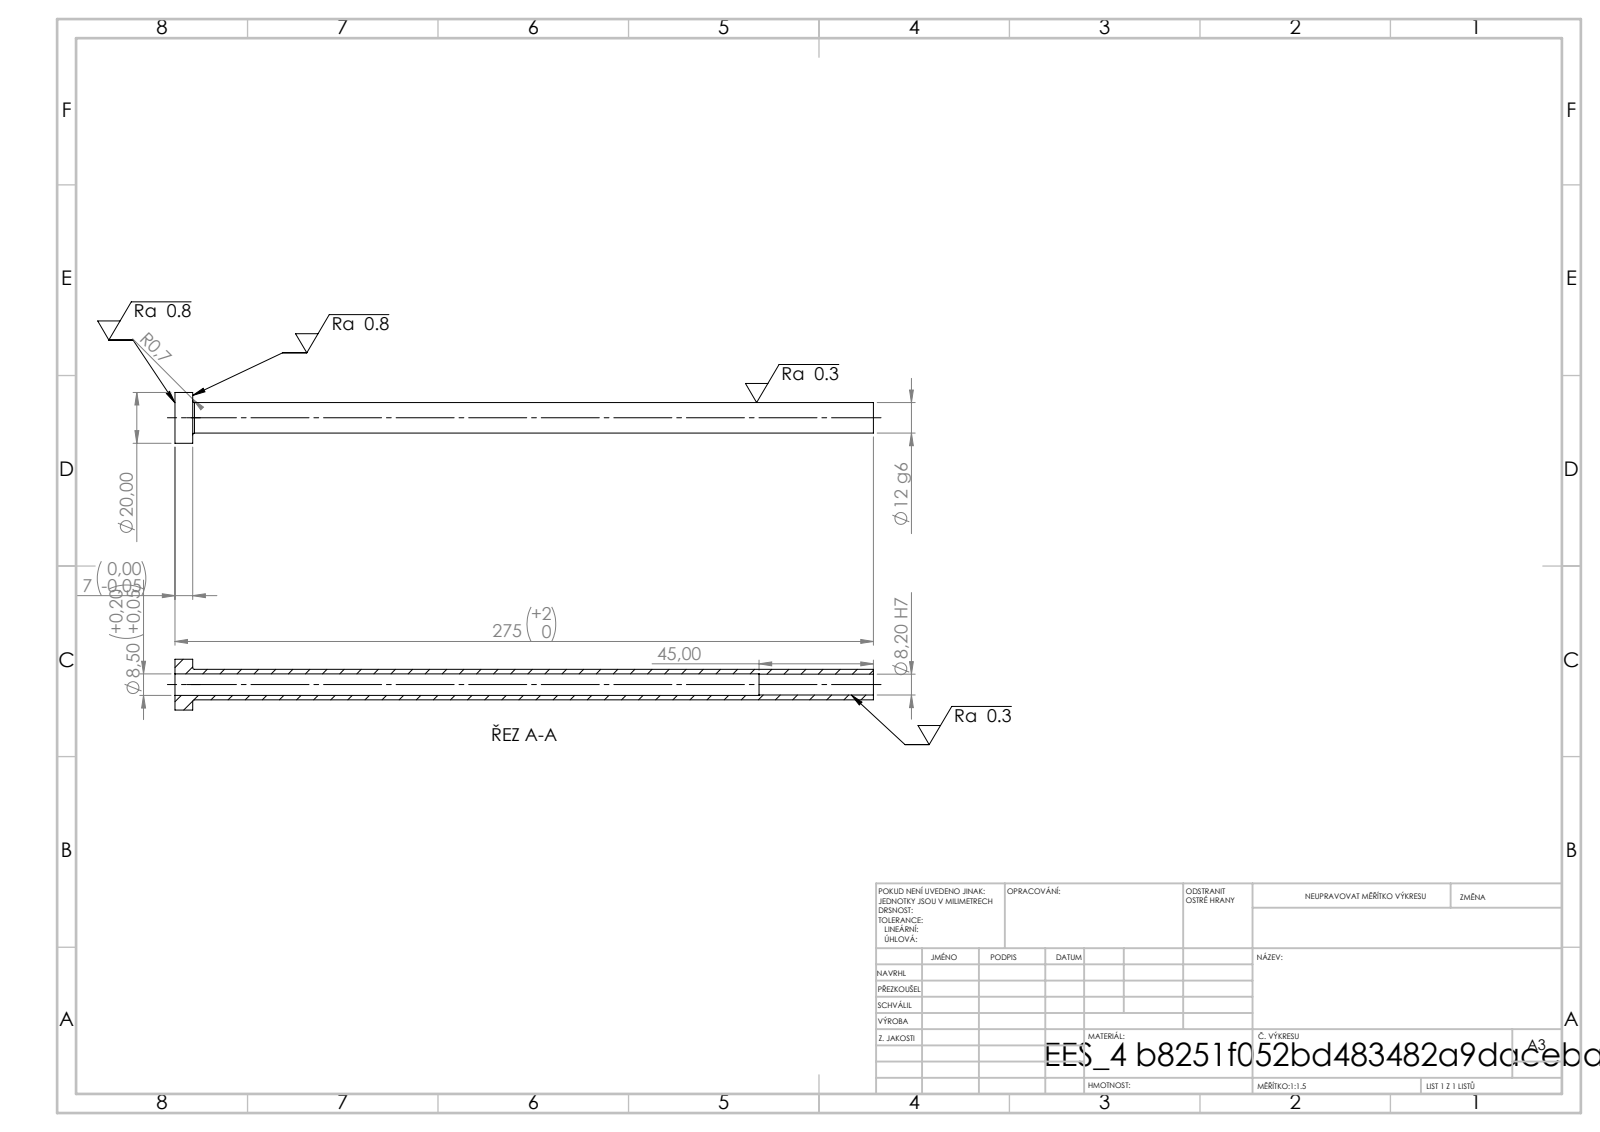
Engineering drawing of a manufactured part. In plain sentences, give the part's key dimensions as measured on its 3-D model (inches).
Its 3-D file was written by "SolidWorks 2019 (CONFIG_CONTROL_DESIGN)". It is 1 solid with 14 faces: 4 planar, 8 cylindrical and 2 other. Overall it measures 10.827 by 0.787 by 0.787 inches. Its volume is 1.043 cubic inches and its surface area 28.45 square inches. Round holes: 1 of diameter 0.323, 1 of diameter 0.335. Round bosses or shafts: 1 of diameter 0.787, 1 of diameter 0.472. The main face-to-face distances are 0.276, 10.827, 10.551, 9.055, 8.78, 1.772.
